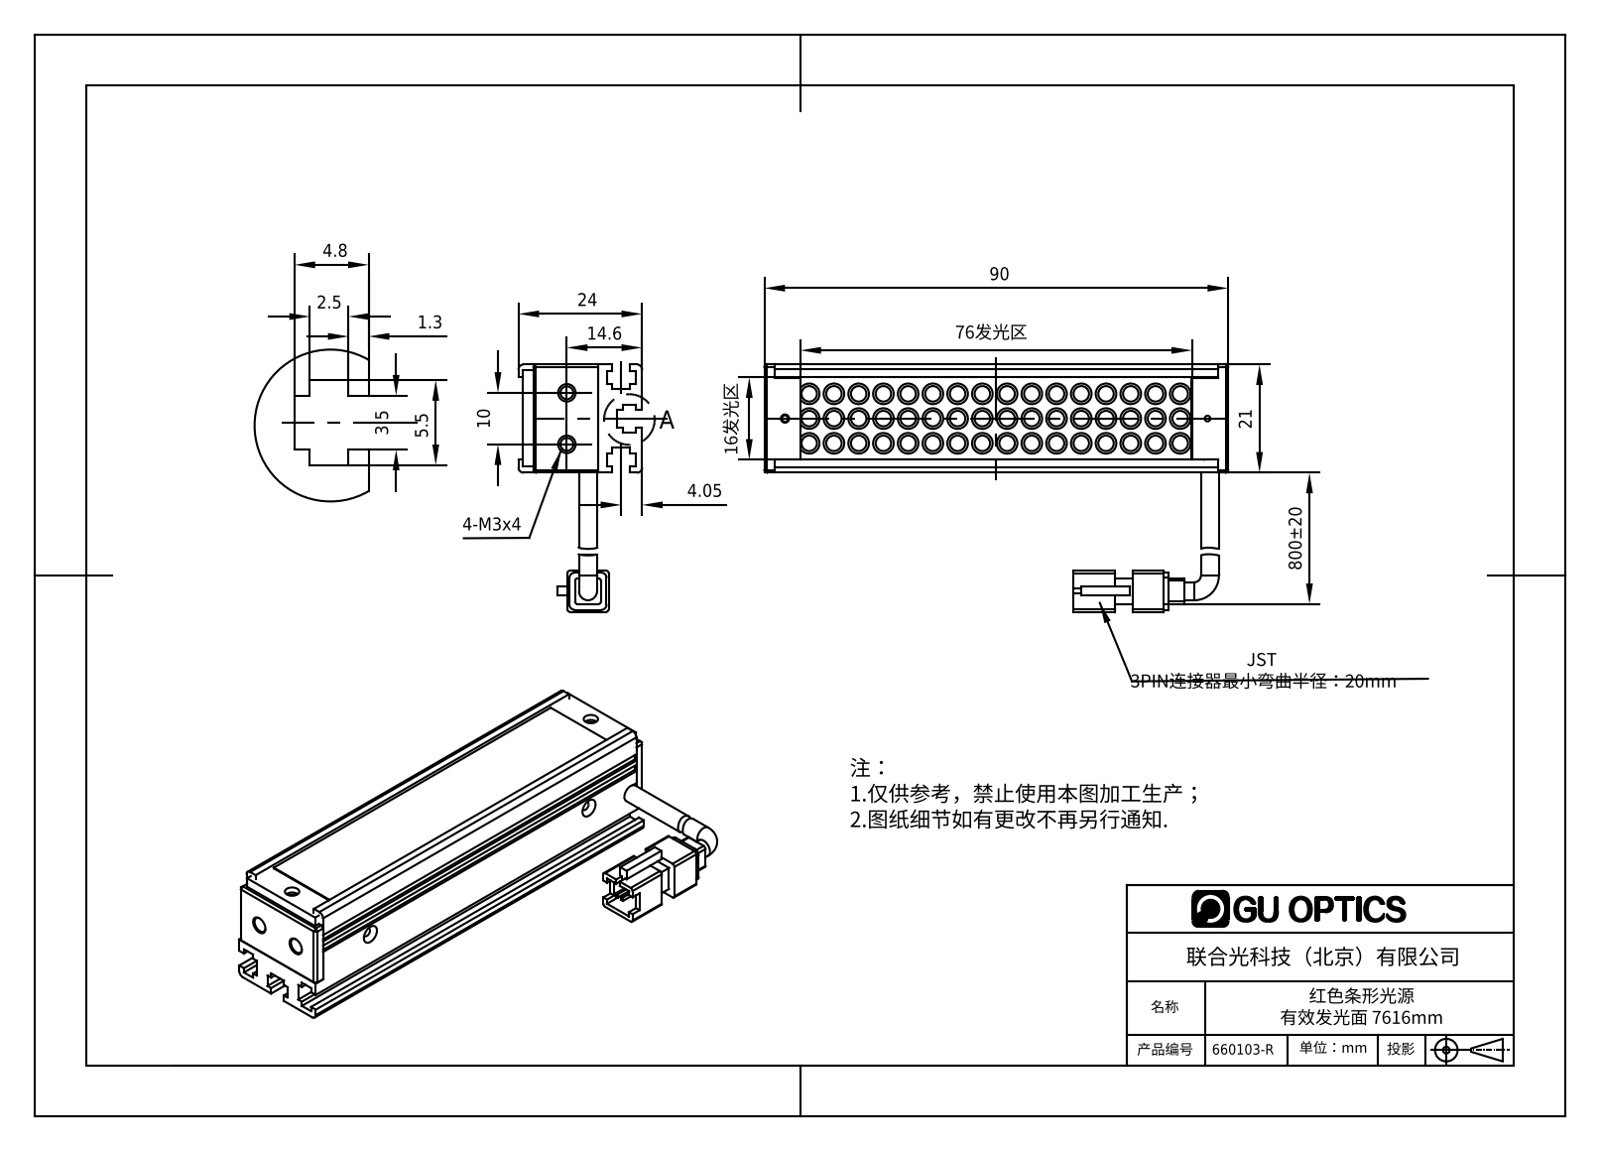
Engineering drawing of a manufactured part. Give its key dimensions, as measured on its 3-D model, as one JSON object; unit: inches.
{"part_name": "660103-R", "step_written_by": "SolidWorks 2016 (AUTOMOTIVE_DESIGN)", "units": "inches", "bodies": {"solids": 8, "faces": 728, "planar": 302, "cylindrical": 275, "other": 151}, "overall_size": [3.543, 1.89, 0.945], "volume_in3": 1.67, "surface_area_in2": 46.86, "round_holes": [[0.063, 5], [0.059, 2], [0.067, 2], [0.098, 2], [0.11, 2], [0.118, 2], [0.043, 1], [0.049, 1], [0.079, 1]], "round_bosses_or_shafts": [[0.157, 48], [0.118, 48], [0.138, 2]], "partial_cylinders_radius": [[0.039, 12], [0.02, 8], [0.065, 1]], "face_to_face_distances": [0.039, 0.079, 0.098, 0.728, 0.575, 0.827, 0.051, 0.138, 0.335, 0.496], "hole_center_spacings": [3.228, 0.276, 0.438, 0.482, 2.796, 2.804, 3.24, 0.394]}
